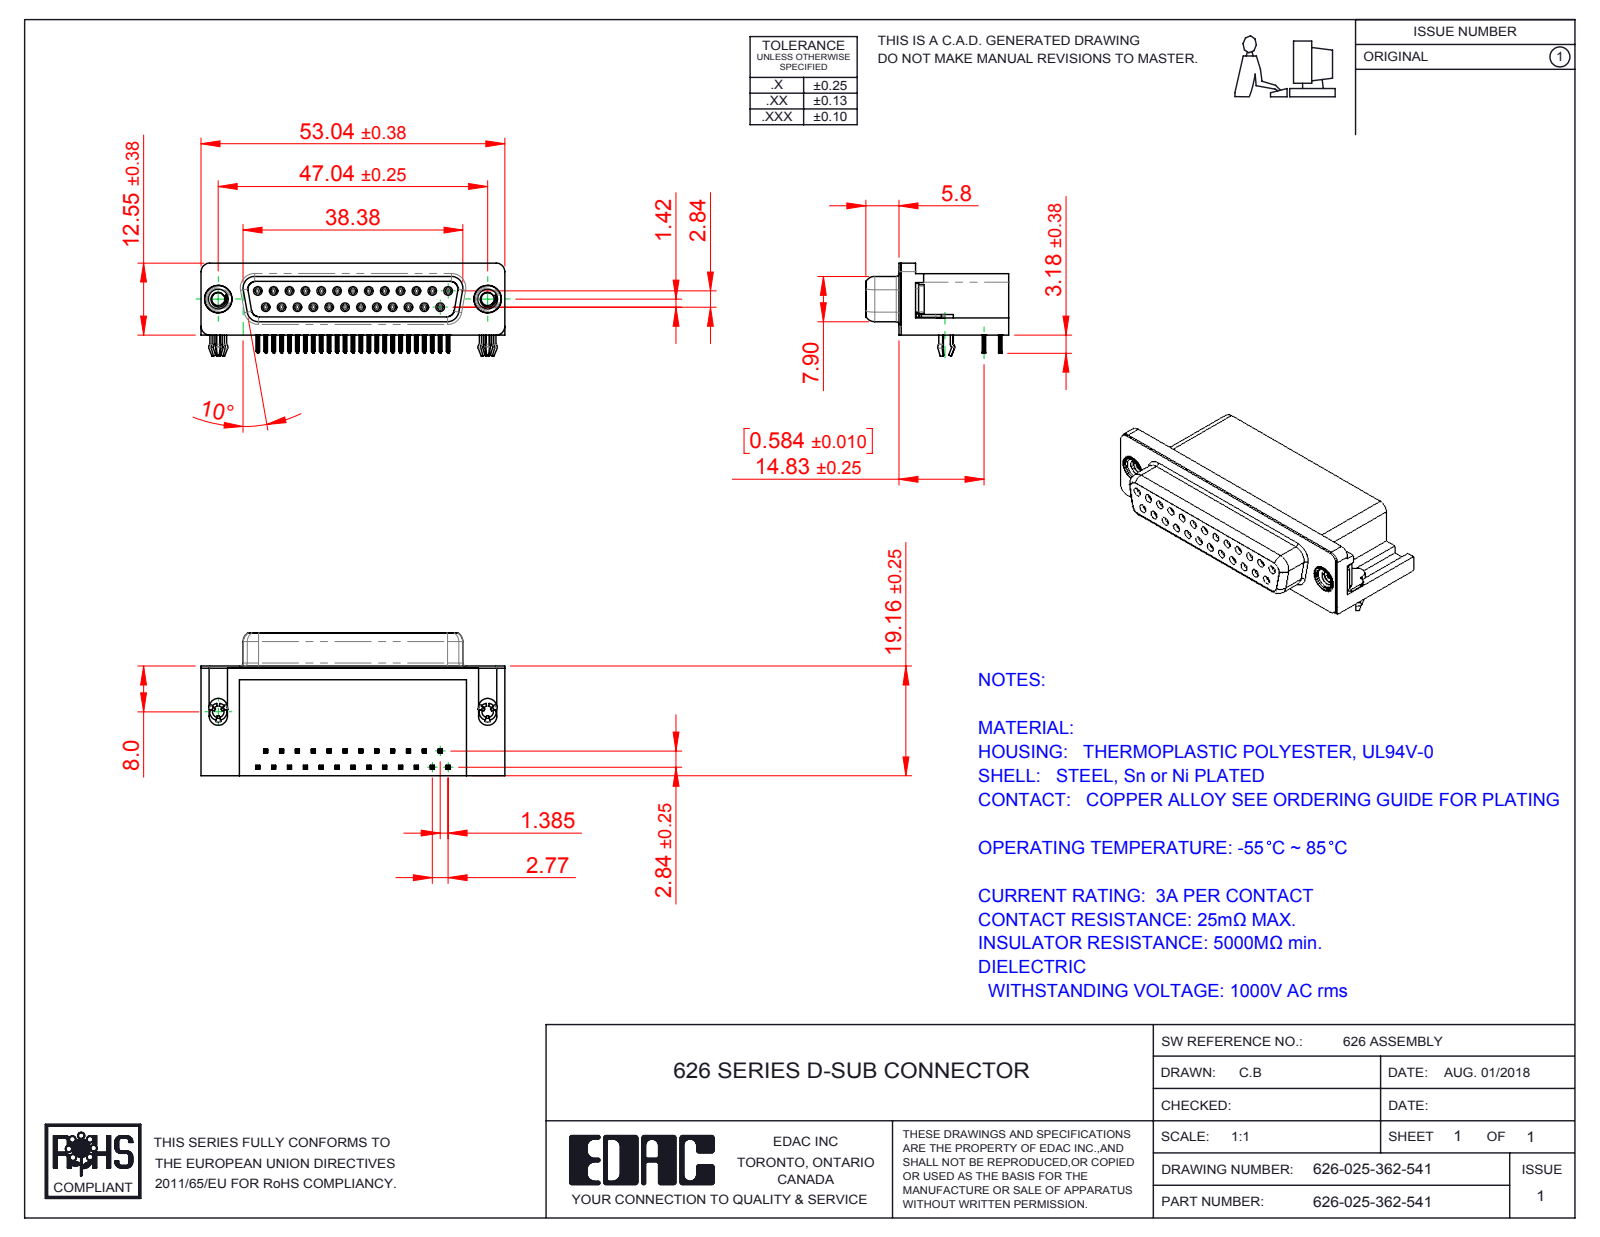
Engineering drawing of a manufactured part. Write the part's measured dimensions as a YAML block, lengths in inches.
part_name: "626 Shell_25 Socket; 626 Housing_25 Socket; 626-025-362-541; 626 4-40 Threaded Rivet (+3 more)"
step_written_by: "SolidWorks 2016 (CONFIG_CONTROL_DESIGN)"
units: inches
bodies: {solids: 31, faces: 3954, planar: 1760, cylindrical: 926, other: 1268}
overall_size: [2.088, 0.983, 0.64]
volume: 0.652
surface_area: 17.71
round_holes:
  - {diameter: 0.031, count: 25}
  - {diameter: 0.035, count: 25}
  - {diameter: 0.079, count: 2}
  - {diameter: 0.089, count: 2}
  - {diameter: 0.157, count: 2}
  - {diameter: 0.189, count: 2}
  - {diameter: 0.197, count: 2}
round_bosses_or_shafts:
  - {diameter: 0.047, count: 25}
  - {diameter: 0.193, count: 2}
  - {diameter: 0.187, count: 2}
  - {diameter: 0.154, count: 2}
  - {diameter: 0.118, count: 2}
partial_cylinders:
  - {radius: 0.004, count: 200}
  - {radius: 0.006, count: 100}
  - {radius: 0.014, count: 50}
  - {radius: 0.013, count: 25}
  - {radius: 0.039, count: 18}
  - {radius: 0.01, count: 12}
  - {radius: 0.011, count: 12}
  - {radius: 0.053, count: 8}
face_to_face_distances: [0.016, 0.407, 0.739, 0.244, 0.107, 0.369, 0.125, 0.033, 0.112, 0.014]
hole_center_spacings: [0.124, 0.109, 0.218, 0.327, 0.436, 0.198, 0.198, 0.294]
